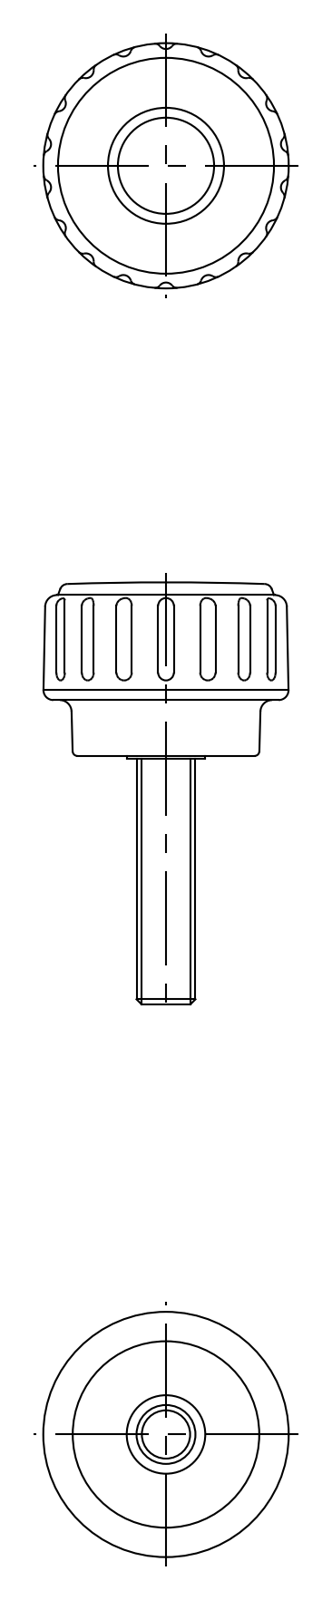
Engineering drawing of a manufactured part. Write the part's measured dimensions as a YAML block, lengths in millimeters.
part_name: "screw; knob; KDMS_25_M6_25_WH_23971_36"
step_written_by: "CADfix (AUTOMOTIVE_DESIGN)"
units: millimeters
bodies: {solids: 2, faces: 110, planar: 0, cylindrical: 0, other: 110}
overall_size: [42.94, 24.96, 24.96]
volume: 7739
surface_area: 3180
